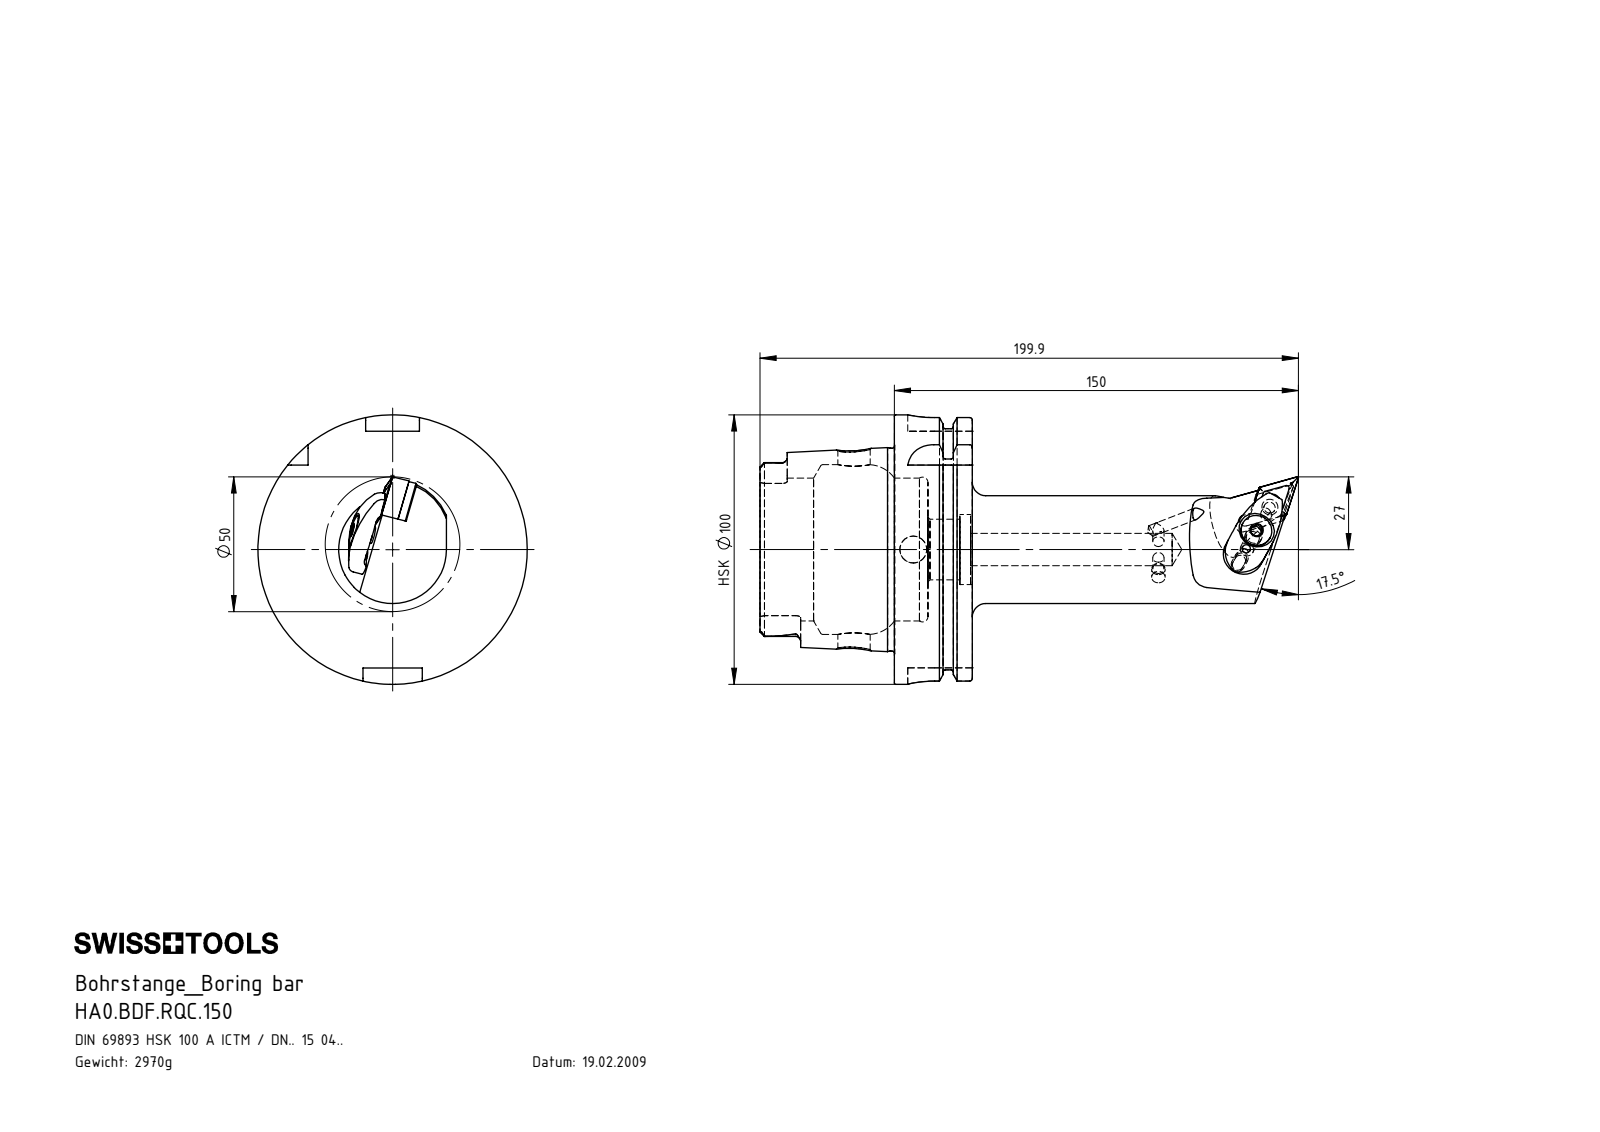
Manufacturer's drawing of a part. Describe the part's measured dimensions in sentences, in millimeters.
The part is named "DNMG150604; WDF-ER2.101.003_A; WCC-ER5.102.005_A; WCC-ER4.102.020_A (+5 more)". Its 3-D file was written by "SolidWorks 2017 (AUTOMOTIVE_DESIGN)". It is 9 solids with 406 faces: 101 planar, 132 cylindrical and 173 other. Overall it measures 199.9 by 100 by 100 millimeters. Its volume is 379 256 cubic millimeters and its surface area 71 143 square millimeters. Round holes: 3 of diameter 4.2, 2 of diameter 5, 2 of diameter 12, 1 of diameter 3, 1 of diameter 4, 1 of diameter 5.16, 1 of diameter 6.5, 1 of diameter 7, 1 of diameter 10, 1 of diameter 22.5, 1 of diameter 26, 1 of diameter 53. Round bosses or shafts: 2 of diameter 5, 1 of diameter 100, 1 of diameter 91.95, 1 of diameter 75.26, 1 of diameter 40, 1 of diameter 11.5, 1 of diameter 7, 1 of diameter 6.2. Partial cylindrical surfaces (rounded edges, fillets, slot ends): 6 of radius 0.39, 6 of radius 0.69, 6 of radius 1.9, 5 of radius 0.4, 4 of radius 10, 2 of radius 2, 2 of radius 3, 2 of radius 4.83. The main face-to-face distances are 28.95, 12.45, 16.5, 49.9, 62.35, 78.85, 87.8, 78.2, 28.3, 15.85. The hole center spacings are 14.8, 15, 23, 8, 8.2.
